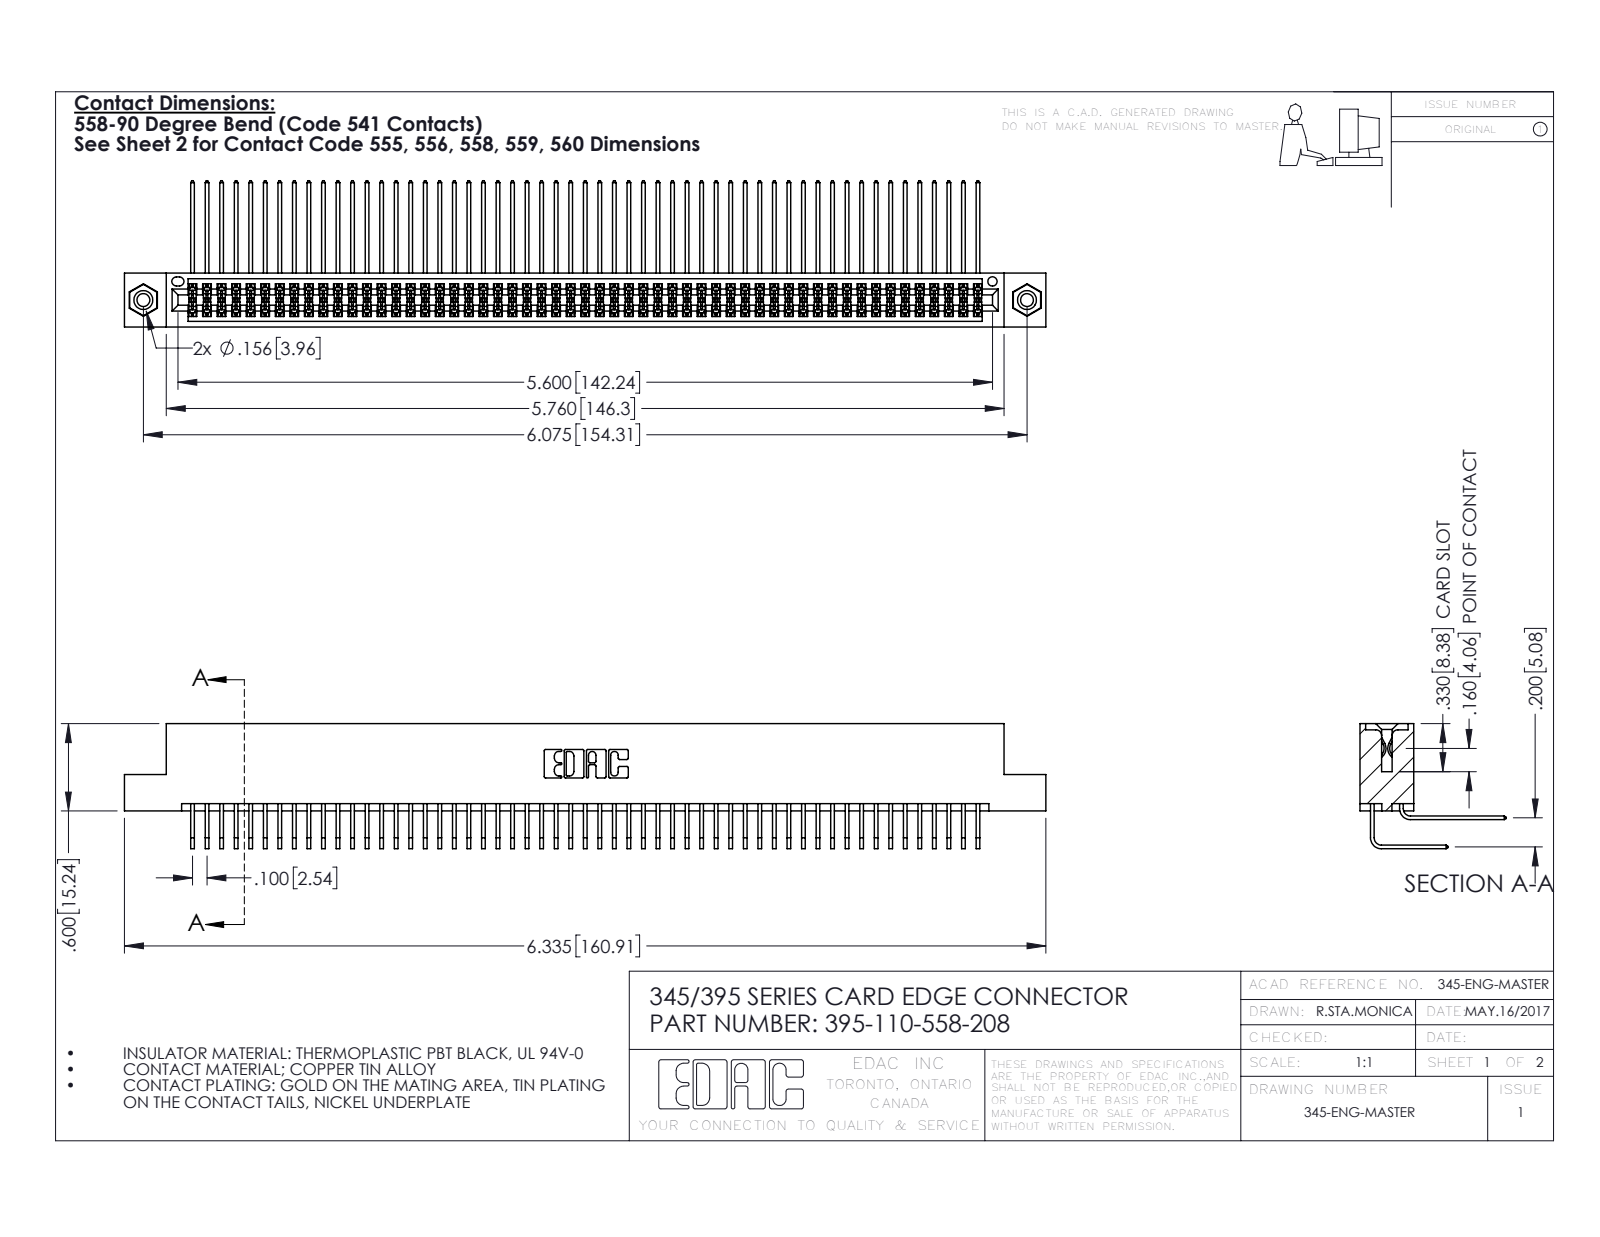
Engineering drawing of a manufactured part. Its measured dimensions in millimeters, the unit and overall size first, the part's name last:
Units: millimetres
Overall size (bounding box): 160.9 × 25.5 × 21.8
Round holes (diameter × count): ⌀2.3 ×2, ⌀3.2 ×2, ⌀4 ×2, ⌀1.6 ×1
Round bosses / shafts (diameter × count): ⌀3.9 ×2
Partial cylindrical surfaces — rounded edges, fillets, slot ends (radius × count): R0.2 ×165, R0.3 ×22, R0.2 ×6, R0.8 ×6, R0.7 ×3, R0.4 ×2, R0.5 ×2, R0.6 ×2
Main face-to-face distances: 1.8, 7.6, 5.1, 9.4, 2.5, 6.9, 0.6, 5.7, 0.6, 4.4
Hole centre spacings: 6.9, 148.3, 154.3
Volume: 16 390 mm³ · Surface area: 27 460 mm²
Bodies: 113 solids, 5906 faces (3962 planar, 1928 cylindrical, 16 other)
Part name (STEP PRODUCT): 395-110-558-208; 345-292-001_558 Tail - 2; 345 Part_Flush Mounting Lugs - 0.156 Dia-TI; 345-292-001_558 559 Tail - 1 (+1 more)
STEP written by: SolidWorks 2016 (CONFIG_CONTROL_DESIGN)
